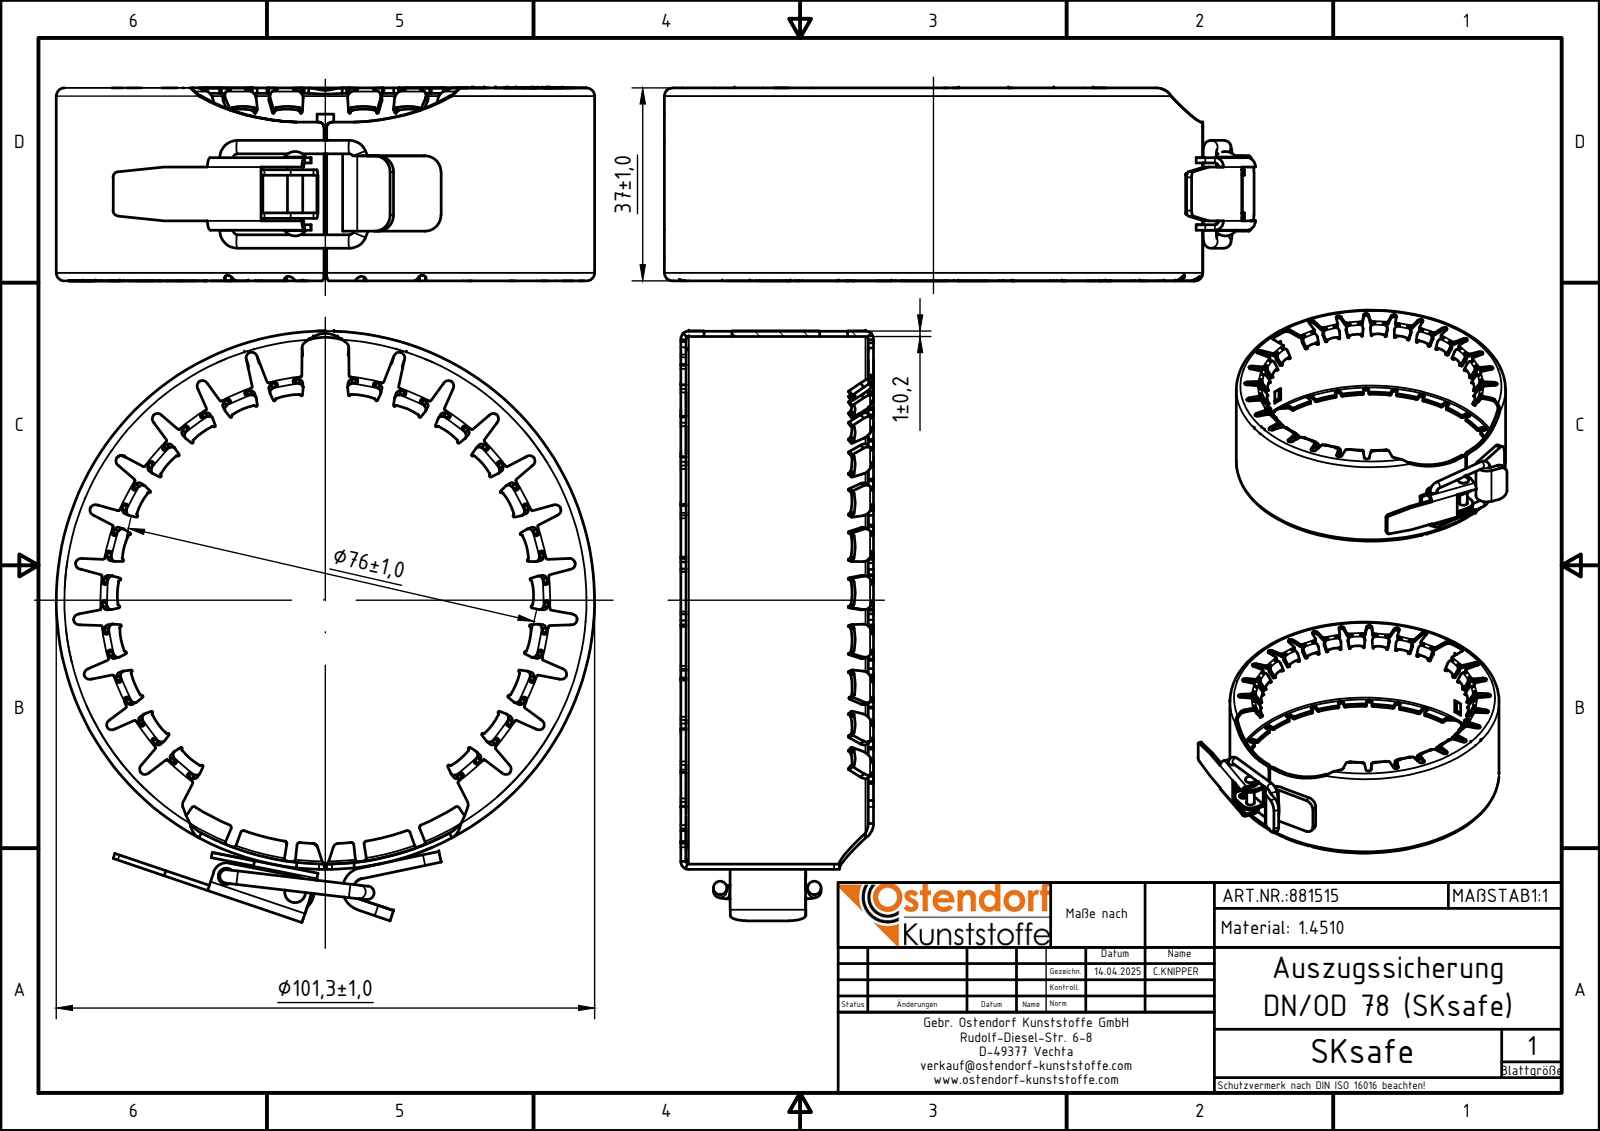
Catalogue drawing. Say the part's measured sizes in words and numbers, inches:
The part is named "881515z". Its 3-D file was written by "Autodesk Inventor 2024 (AUTOMOTIVE_DESIGN)". It is 6 solids with 1340 faces: 128 planar, 101 cylindrical and 1111 other. Overall it measures 4.322 by 3.935 by 1.41 inches. Its volume is 0.946 cubic inches and its surface area 49.18 square inches. Round holes: 3 of diameter 0.118, 1 of diameter 3.856. Round bosses or shafts: 3 of diameter 0.098, 1 of diameter 3.935, 1 of diameter 0.11. Partial cylindrical surfaces (rounded edges, fillets, slot ends): 8 of radius 0.078, 5 of radius 0.078, 5 of radius 0.118, 4 of radius 0.039, 4 of radius 0.078, 3 of radius 0.078, 2 of radius 0.029, 2 of radius 0.069. The main face-to-face distances are 0.039, 0.079, 0.37, 0.861, 0.491, 0.315, 0.457, 0.087, 0.404, 0.772. The hole center spacings are 0.197, 0.317, 0.515, 2.13, 2.143, 2.147.
